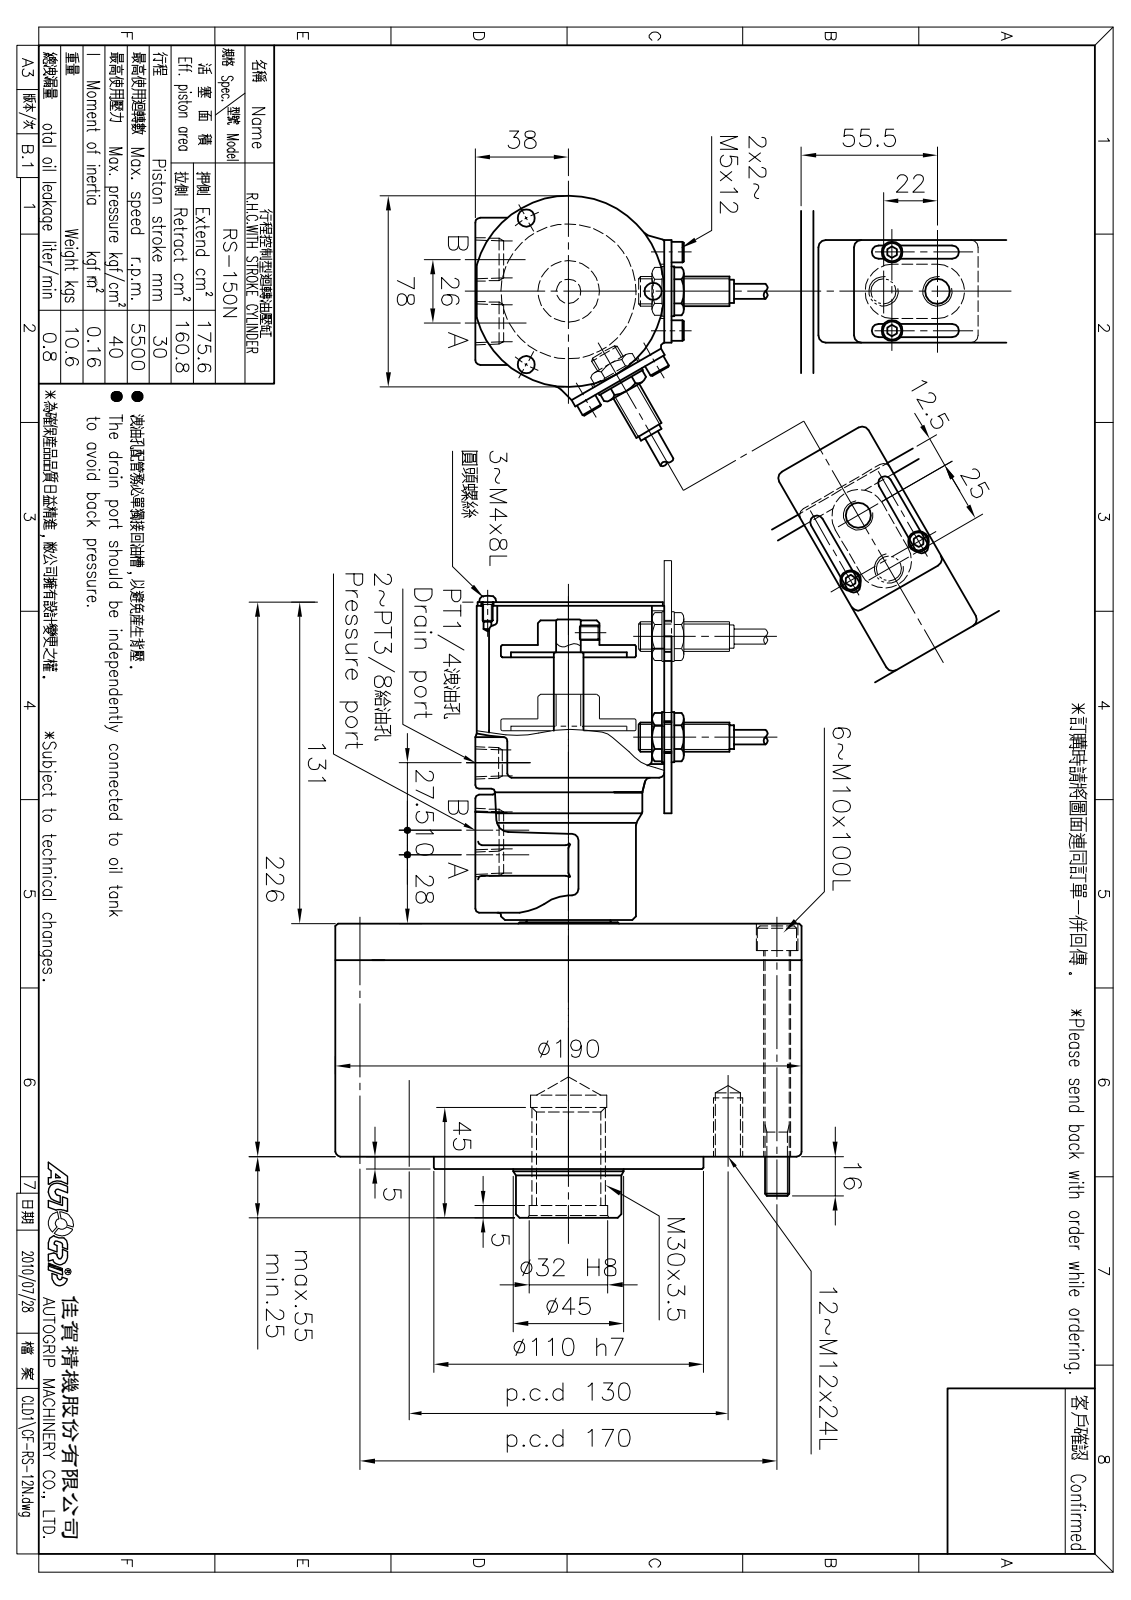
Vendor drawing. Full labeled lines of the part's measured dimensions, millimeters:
Part name (STEP PRODUCT): RS-100 行控盒蓋板; RS-100 感應器定位板; RS-100行控盒; RS-150活塞 (+3 more)
STEP written by: SolidWorks 2016 (CONFIG_CONTROL_DESIGN)
Units: millimetres
Bodies: 10 solids, 455 faces (135 planar, 220 cylindrical, 100 other)
Overall size (bounding box): 265.15 × 190 × 190
Volume: 2 702 000 mm³ · Surface area: 383 081 mm²
Round holes (diameter × count): ⌀12 ×13, ⌀10.2 ×12, ⌀5 ×8, ⌀11 ×6, ⌀17 ×6, ⌀4.1 ×4, ⌀12.5 ×2, ⌀14.7 ×2, ⌀8 ×1, ⌀25 ×1, ⌀30 ×1, ⌀32 ×1
Round bosses / shafts (diameter × count): ⌀12 ×2, ⌀10.2 ×2, ⌀7.2 ×2, ⌀3.7 ×2, ⌀190 ×1, ⌀150 ×1, ⌀110 ×1, ⌀77 ×1
Partial cylindrical surfaces — rounded edges, fillets, slot ends (radius × count): R3 ×12, R1.5 ×8, R2.75 ×8, R9 ×4, R11 ×4, R5 ×2, R6 ×2, R15 ×2
Main face-to-face distances: 15, 7, 22, 10.41, 17.41, 32.41, 50, 43, 30, 65
Hole centre spacings: 65, 92.68, 85, 112.59, 148.74, 27.87, 33.65, 41.49
